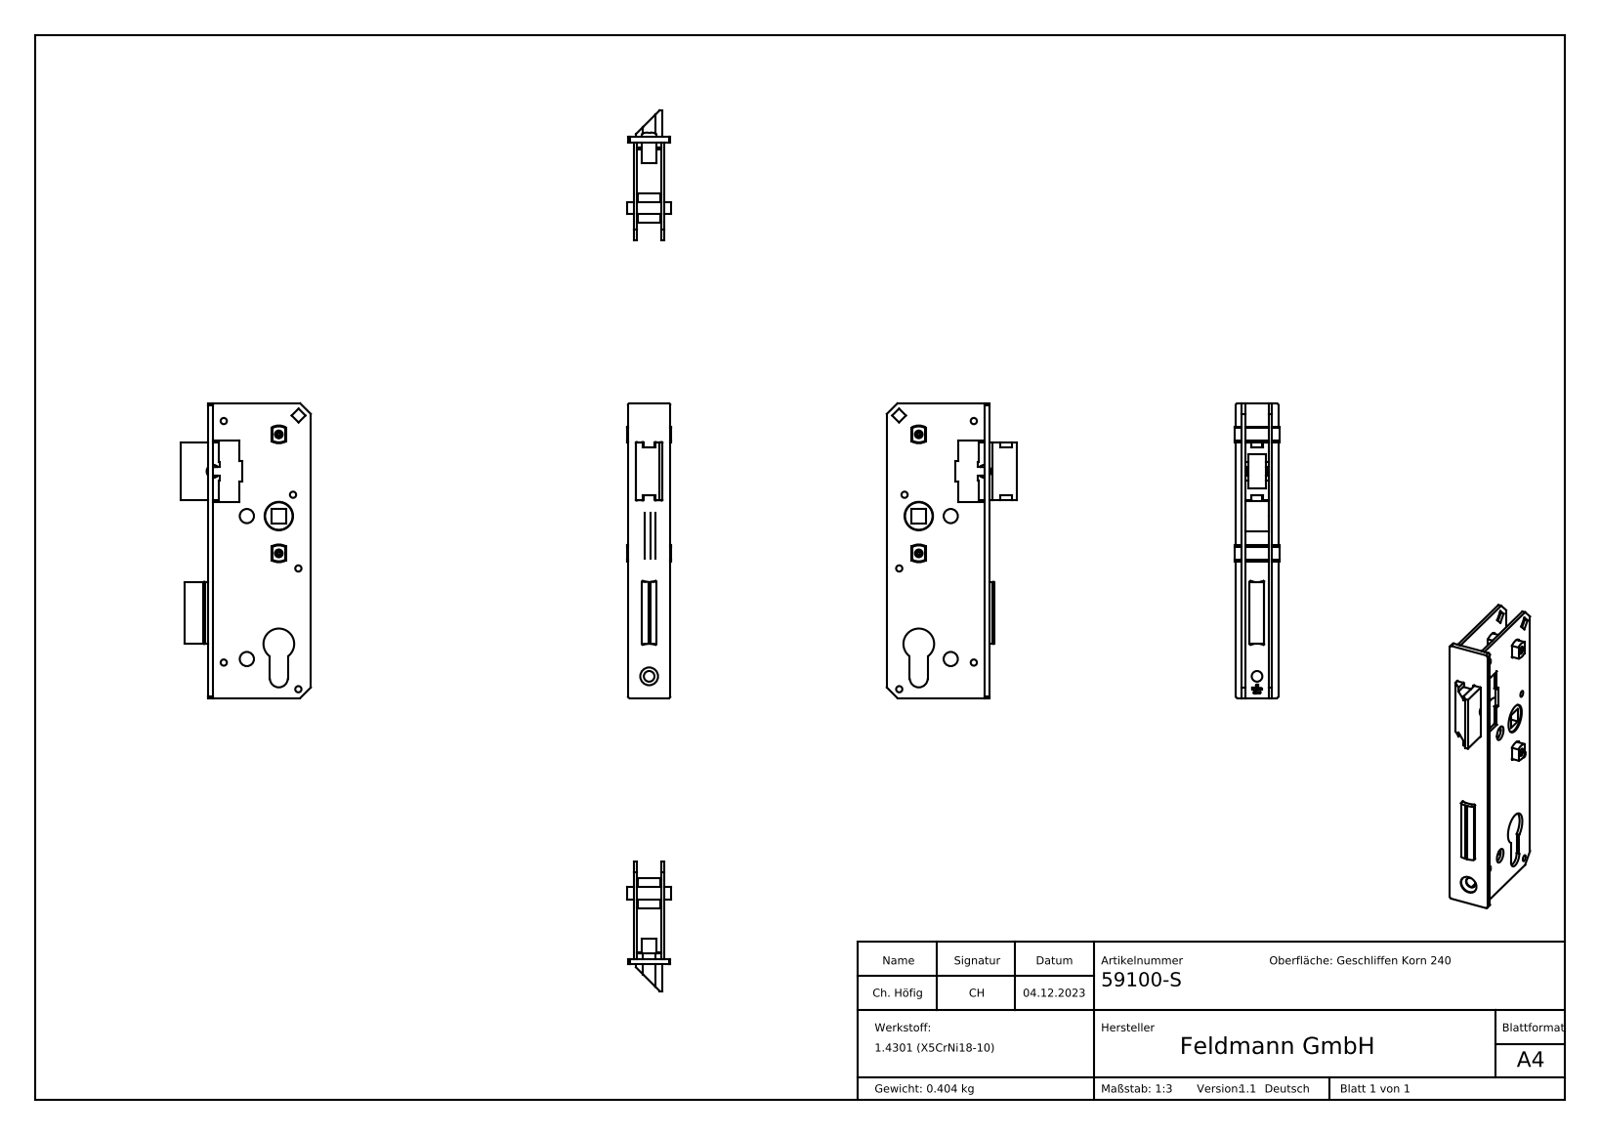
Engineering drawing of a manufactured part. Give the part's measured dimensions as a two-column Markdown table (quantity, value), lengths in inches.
| quantity | value |
| --- | --- |
| part name | Schlosskasten Teil5 Konfig_59XXX-240 Teil5; Schlosskasten Teil4 Konfig_59XXX-240 Teil4; Schlosskasten Teil3 Konfig_59XXX-240 Teil3; Schlosskasten Teil2 Konfig_59100-240 Teil2 (+1 more) |
| STEP written by | SolidWorks 2018 (CONFIG_CONTROL_DESIGN) |
| units | inches |
| bodies | 8 solids, 450 faces (248 planar, 71 cylindrical, 131 other) |
| overall size | 6.535 × 2.874 × 0.984 |
| volume | 3.113 in³ |
| surface area | 78.02 in² |
| round holes (diameter × count) | 0.138 × 5, 0.13 × 2, 0.315 × 2, 0.236 × 1, 0.394 × 1, 0.63 × 1, 0.681 × 1 |
| round bosses / shafts (diameter × count) | 0.669 × 1, 0.61 × 1 |
| partial cylindrical surfaces (radius × count) | 0.012 × 8, 0.024 × 8, 0.02 × 4, 0.039 × 4, 0.173 × 4, 0.295 × 4, 0.315 × 4, 0.094 × 1 |
| main face-to-face distances | 0.069, 0.6, 0.669, 0.531, 0.118, 0.807, 0.138, 0.207, 0.738, 0.134 |
| hole center spacings | 0.518, 0.547, 0.568, 0.709, 0.784, 0.827, 1.089, 1.093 |
